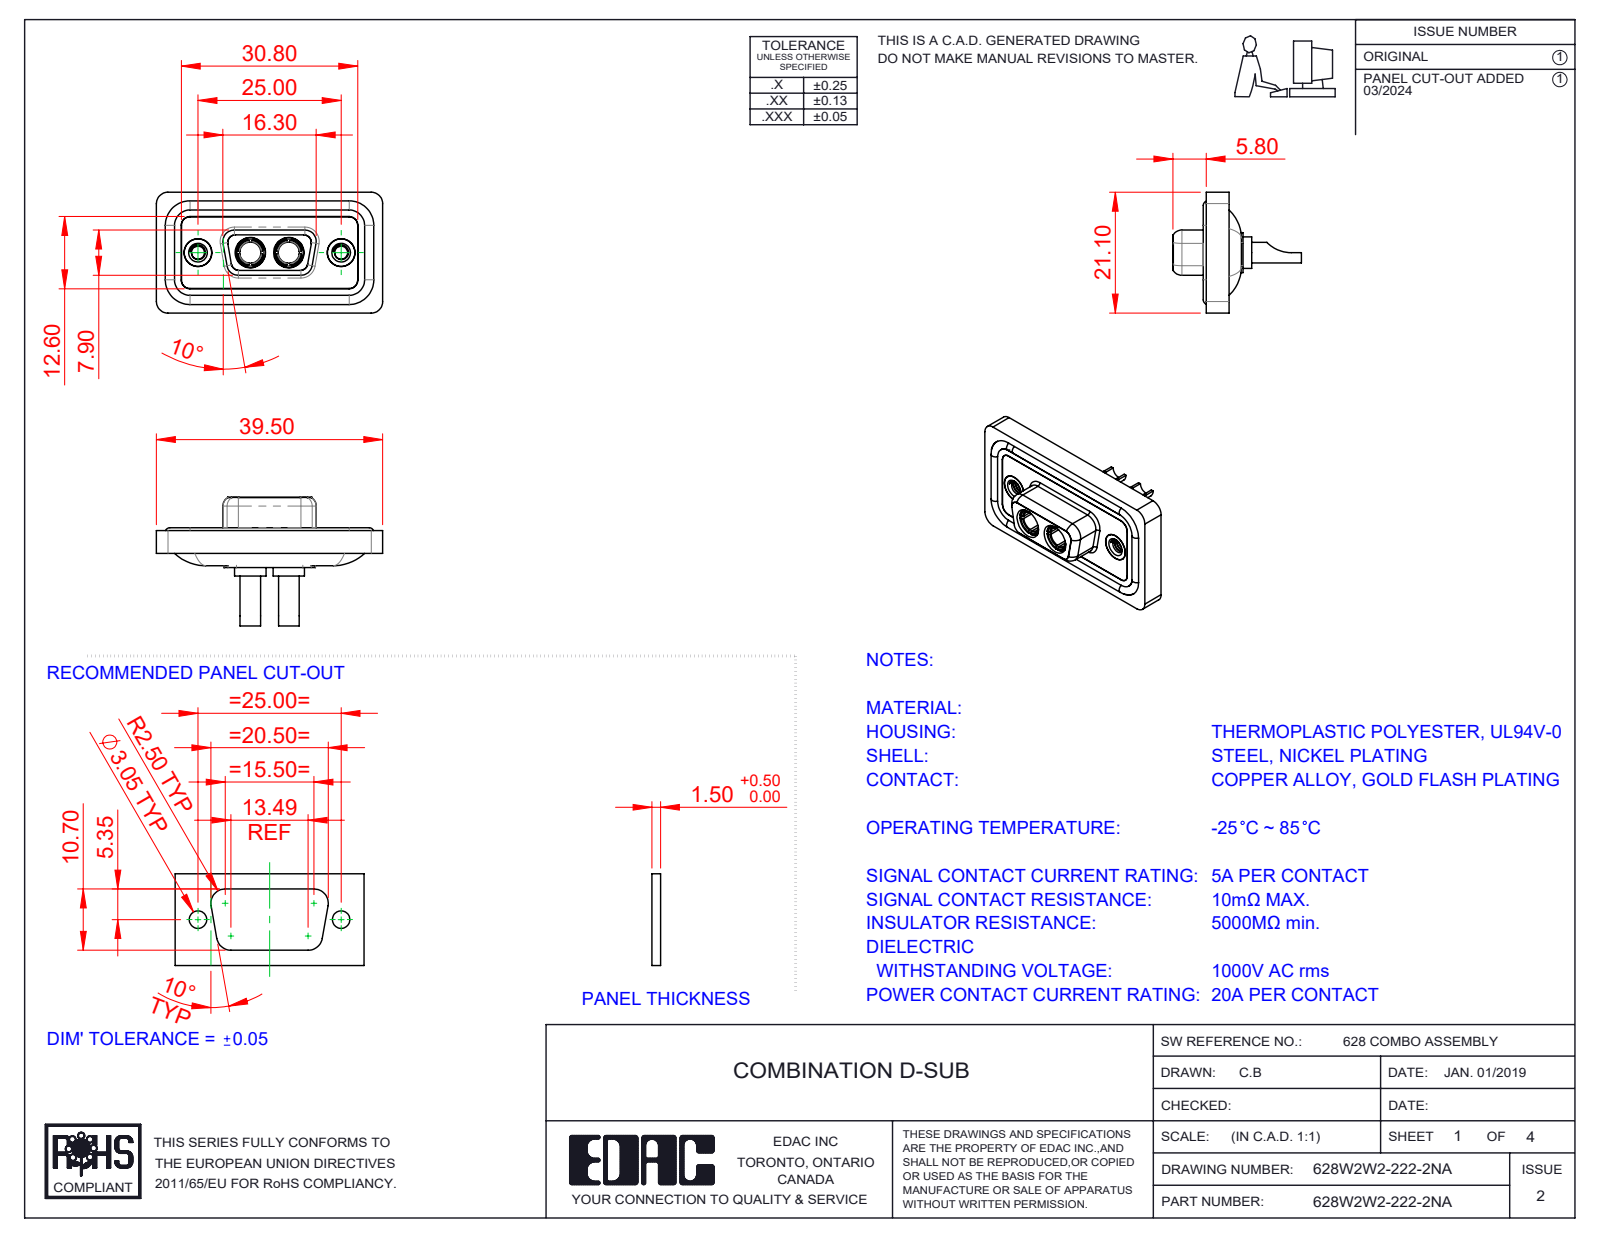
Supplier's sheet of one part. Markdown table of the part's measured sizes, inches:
| quantity | value |
| --- | --- |
| part name | 628Combo Waterproof Housing_09 Contacts; 628Combo Shell Rear_09 Contacts; 628Combo Threaded Rivet_A; 628W2W2-222-2NA (+3 more) |
| STEP written by | SolidWorks 2023 (CONFIG_CONTROL_DESIGN) |
| units | inches |
| bodies | 11 solids, 544 faces (169 planar, 242 cylindrical, 133 other) |
| overall size | 1.555 × 0.884 × 0.831 |
| volume | 0.289 in³ |
| surface area | 12.09 in² |
| round holes (diameter × count) | 0.191 × 4, 0.089 × 2, 0.106 × 2, 0.146 × 2, 0.157 × 2, 0.159 × 2, 0.197 × 2, 0.209 × 2 |
| round bosses / shafts (diameter × count) | 0.063 × 4, 0.217 × 2, 0.205 × 2, 0.195 × 2, 0.195 × 2, 0.189 × 2, 0.187 × 2, 0.148 × 2 |
| partial cylindrical surfaces (radius × count) | 0.059 × 22, 0.079 × 18, 0.053 × 8, 0.063 × 8, 0.01 × 4, 0.02 × 4, 0.024 × 4, 0.026 × 4 |
| main face-to-face distances | 0.016, 0.071, 0.043, 0.114, 0.02, 0.063, 0.222, 0.293, 0.211, 0.059 |
| hole center spacings | 0.36, 0.624, 0.265, 0.984 |
